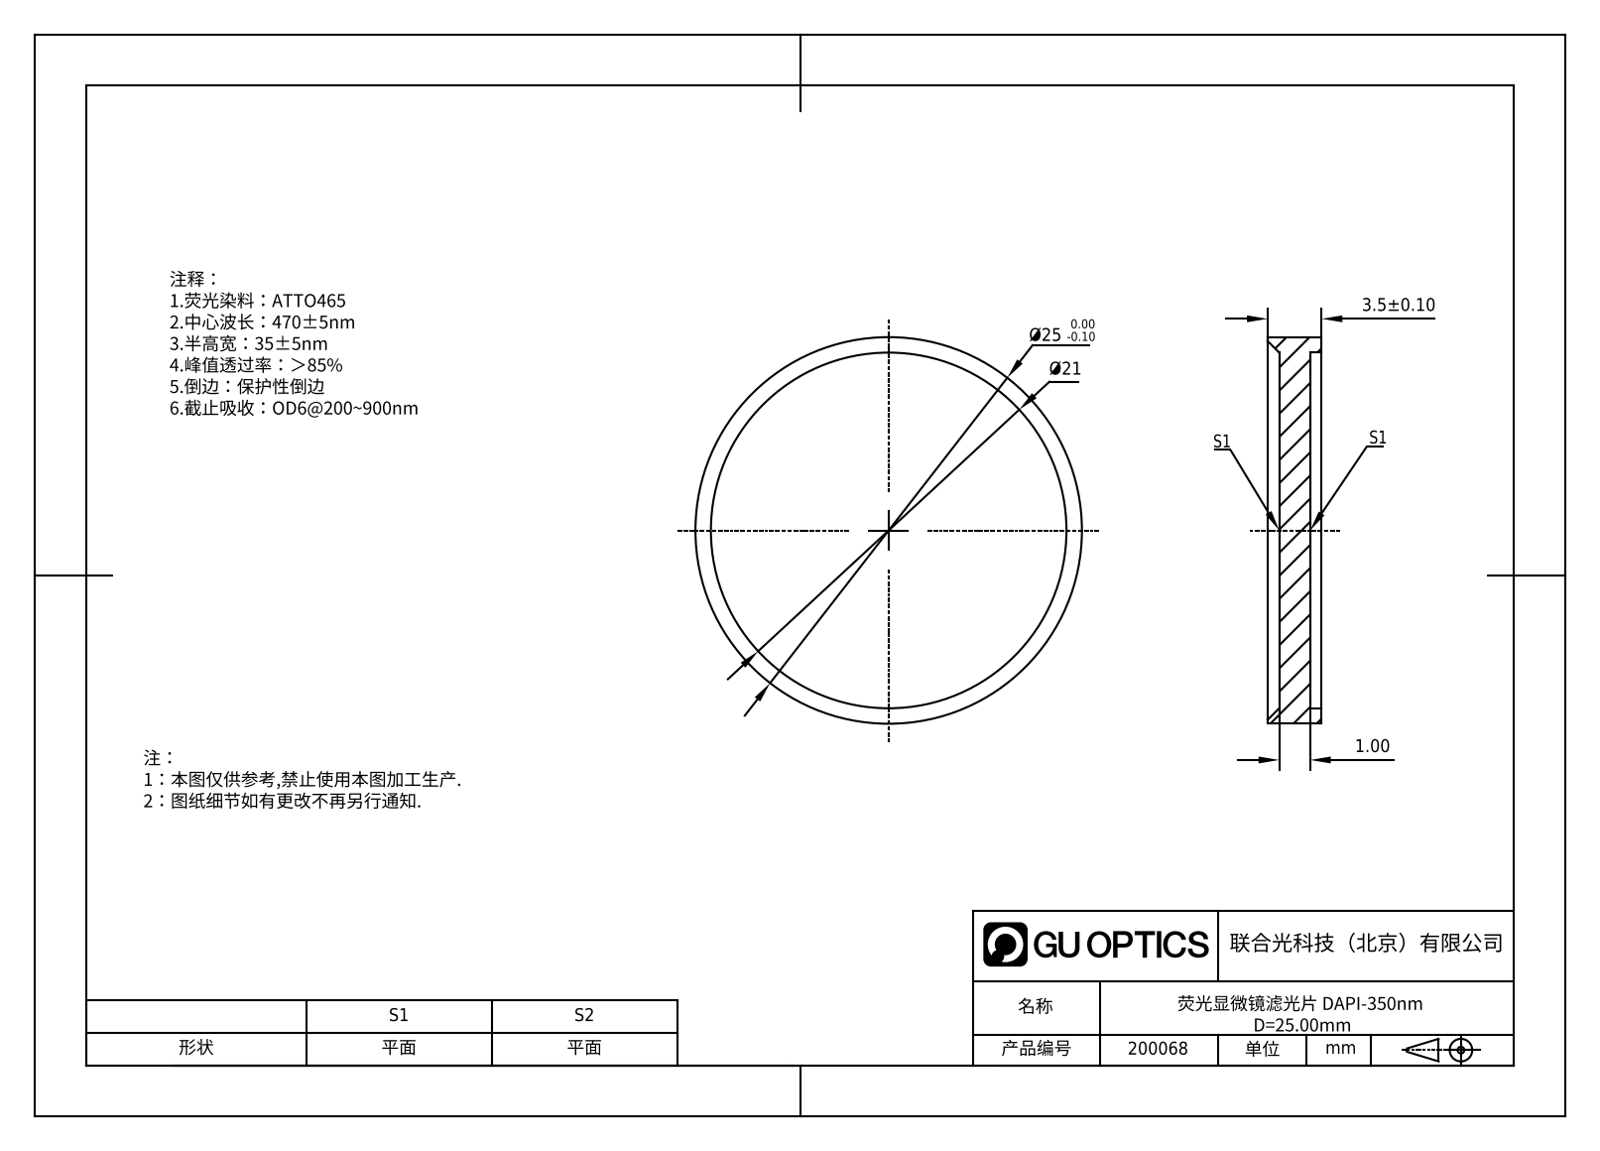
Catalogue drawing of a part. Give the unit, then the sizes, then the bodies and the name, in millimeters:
Units: millimetres
Overall size (bounding box): 25 × 25 × 3.5
Round holes (diameter × count): ⌀23 ×1
Round bosses / shafts (diameter × count): ⌀25 ×1
Main face-to-face distances: 2, 0.75, 2.75, 3.5
Volume: 1 074 mm³ · Surface area: 1 334 mm²
Bodies: 1 solid, 10 faces (4 planar, 4 cylindrical, 2 other)
Part name (STEP PRODUCT): GNIF-045-350-D25
STEP written by: SolidWorks 2022 (AUTOMOTIVE_DESIGN)
